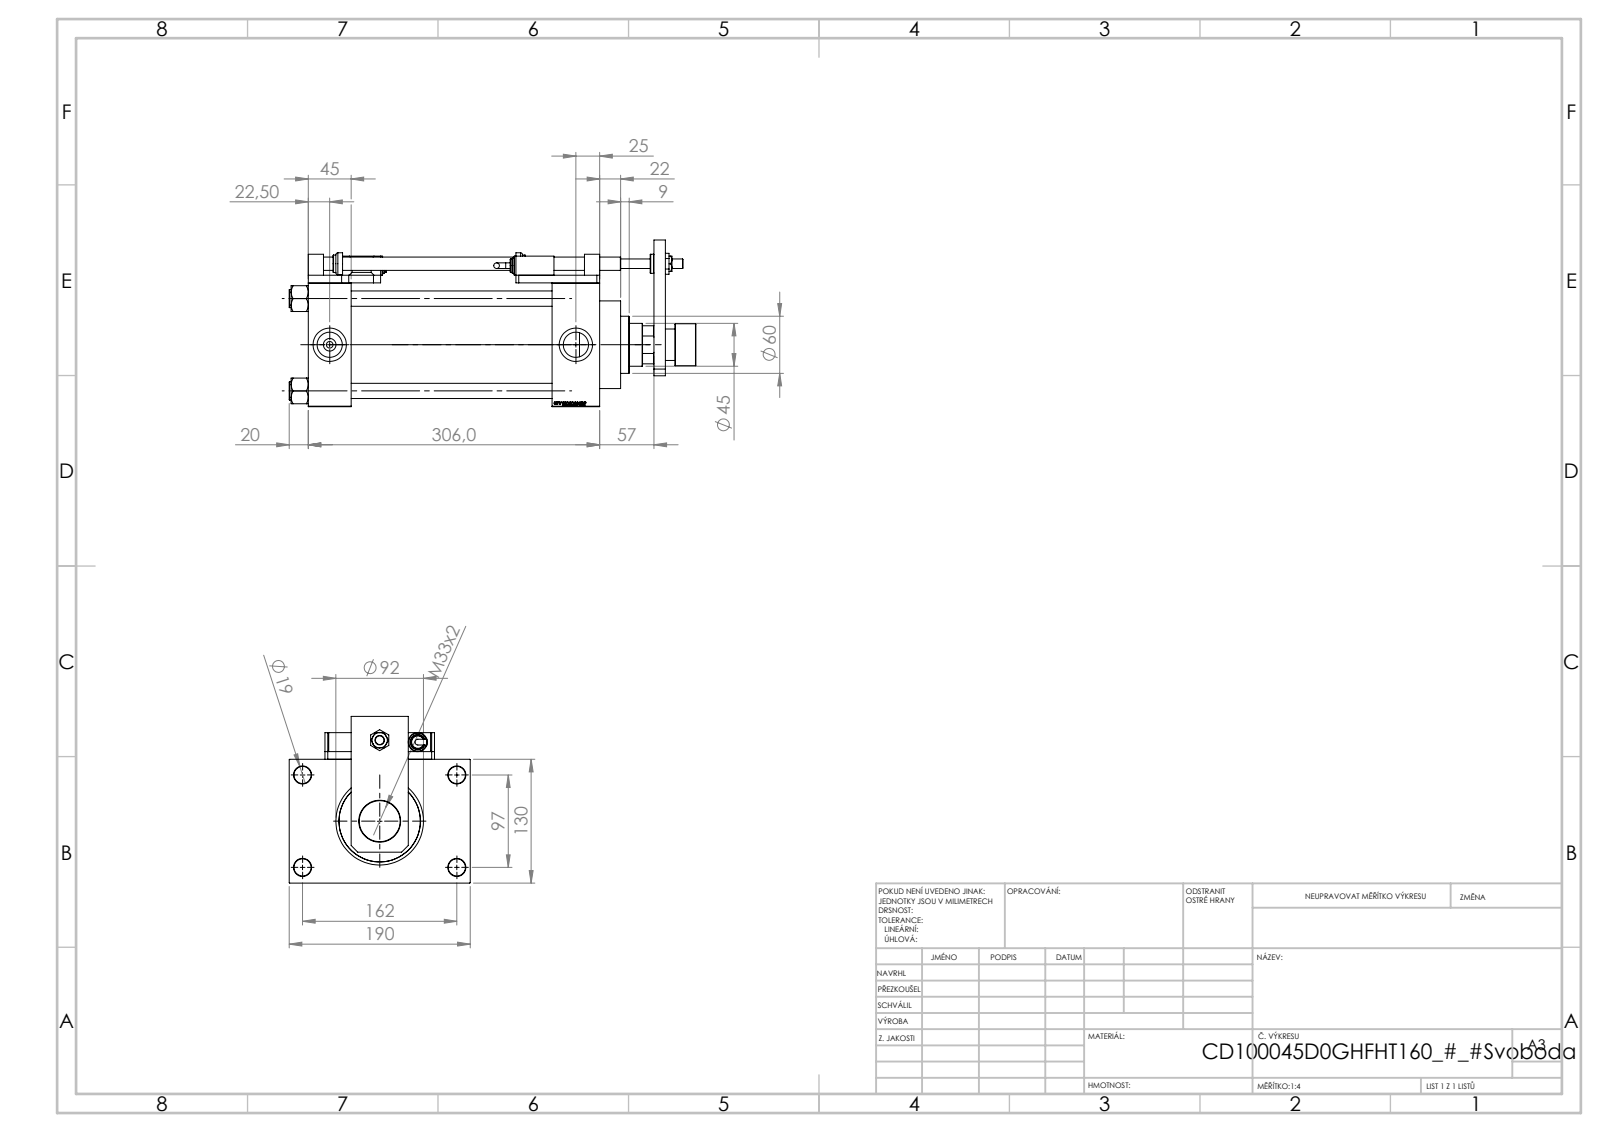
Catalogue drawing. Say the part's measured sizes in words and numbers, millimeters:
The part is named "V215CD_SWITCH_Q_PODLOZKA_FRONT; V215CD_SWITCH_Q_MAGNET; V215CR_ROD_END_F; V215CD_D_Body (+7 more)". Its 3-D file was written by "SolidWorks 2019 (CONFIG_CONTROL_DESIGN)". It is 25 solids with 1392 faces: 669 planar, 160 cylindrical and 563 other. Overall it measures 427 by 190 by 175 millimeters. Its volume is 3 464 000 cubic millimeters and its surface area 605 173 square millimeters. Round holes: 4 of diameter 8.5, 4 of diameter 13.5, 4 of diameter 16, 4 of diameter 18, 2 of diameter 7, 2 of diameter 26.44, 2 of diameter 35, 1 of diameter 10, 1 of diameter 14, 1 of diameter 31.5, 1 of diameter 33, 1 of diameter 45. Round bosses or shafts: 4 of diameter 19, 3 of diameter 20, 2 of diameter 16, 2 of diameter 14, 2 of diameter 6, 1 of diameter 106, 1 of diameter 92, 1 of diameter 60. Partial cylindrical surfaces (rounded edges, fillets, slot ends): 4 of radius 7.5. The main face-to-face distances are 45, 130, 261, 306, 8, 50, 160, 256, 211, 138. The hole center spacings are 32.55, 68.52, 94.41, 96.9, 102.27, 129.45, 161.73, 32.
